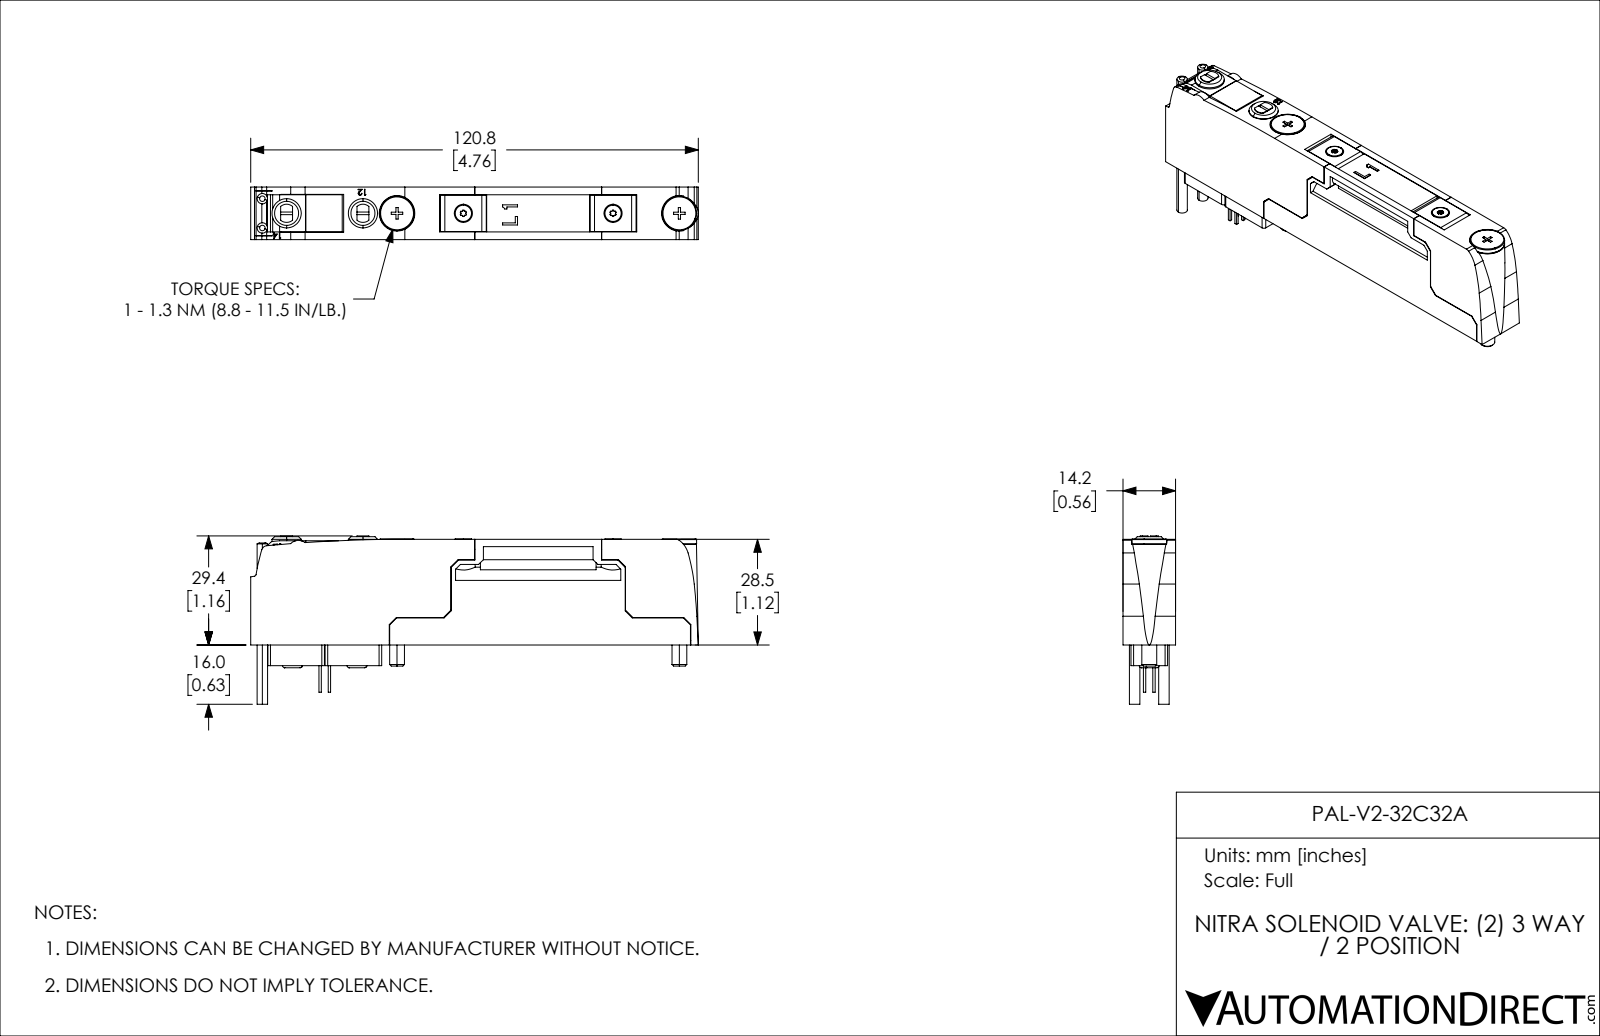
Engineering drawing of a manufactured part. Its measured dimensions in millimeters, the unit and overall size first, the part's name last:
Units: millimetres
Overall size (bounding box): 120.8 × 45.4 × 14.2
Round holes (diameter × count): ⌀3.1 ×2, ⌀4.2 ×2, ⌀9.6 ×1
Round bosses / shafts (diameter × count): ⌀9.3 ×2, ⌀7.9 ×2, ⌀4.4 ×2, ⌀4 ×2, ⌀2.8 ×2
Partial cylindrical surfaces — rounded edges, fillets, slot ends (radius × count): R0.7 ×8, R0.72 ×4, R1.2 ×4, R1.5 ×3, R0.65 ×2, R0.88 ×2, R1.95 ×2, R2.2 ×2
Main face-to-face distances: 14.2, 2.1, 12.1, 2.2, 6.4, 28.5, 17.2, 10, 5.6, 21.2
Hole centre spacings: 10.8, 17.4, 28.2, 76.2, 87, 104.4
Volume: 44 729 mm³ · Surface area: 18 020 mm²
Bodies: 1 solid, 555 faces (397 planar, 121 cylindrical, 37 other)
Part name (STEP PRODUCT): PAL-V2-32C32A
STEP written by: SolidWorks 2019 (CONFIG_CONTROL_DESIGN)
